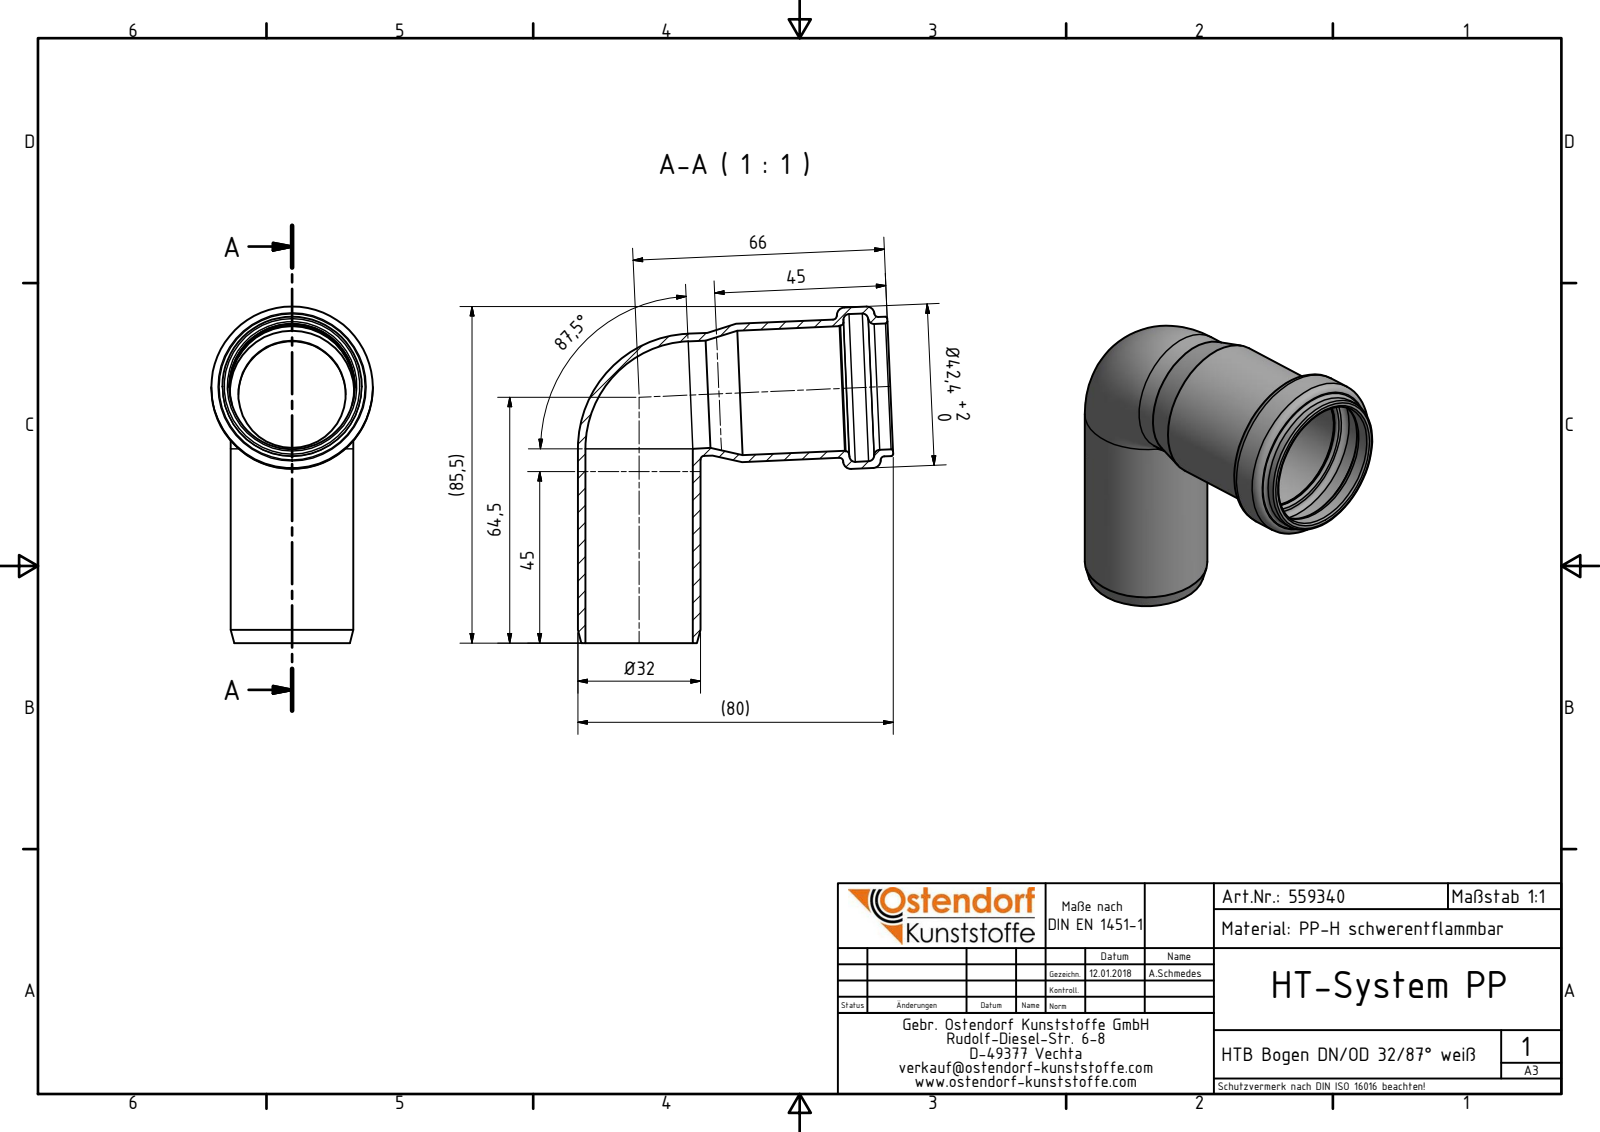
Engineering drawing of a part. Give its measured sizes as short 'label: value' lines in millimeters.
name: 559340 HTB DN_OD 32_87° weiß
written by: Autodesk Inventor 2016 (AUTOMOTIVE_DESIGN)
unit: mm
bodies: 1 solid, 34 faces (3 planar, 11 cylindrical, 20 other)
size: 88.33 × 82.81 × 42.4
volume: 24 228 mm³; area: 26 335 mm²
holes: 2× ⌀28.2, 1× ⌀32.7, 1× ⌀33, 1× ⌀38.8
bosses: 2× ⌀32.2, 1× ⌀42.4, 1× ⌀36.6, 1× ⌀36.3
face distances: 12.63
